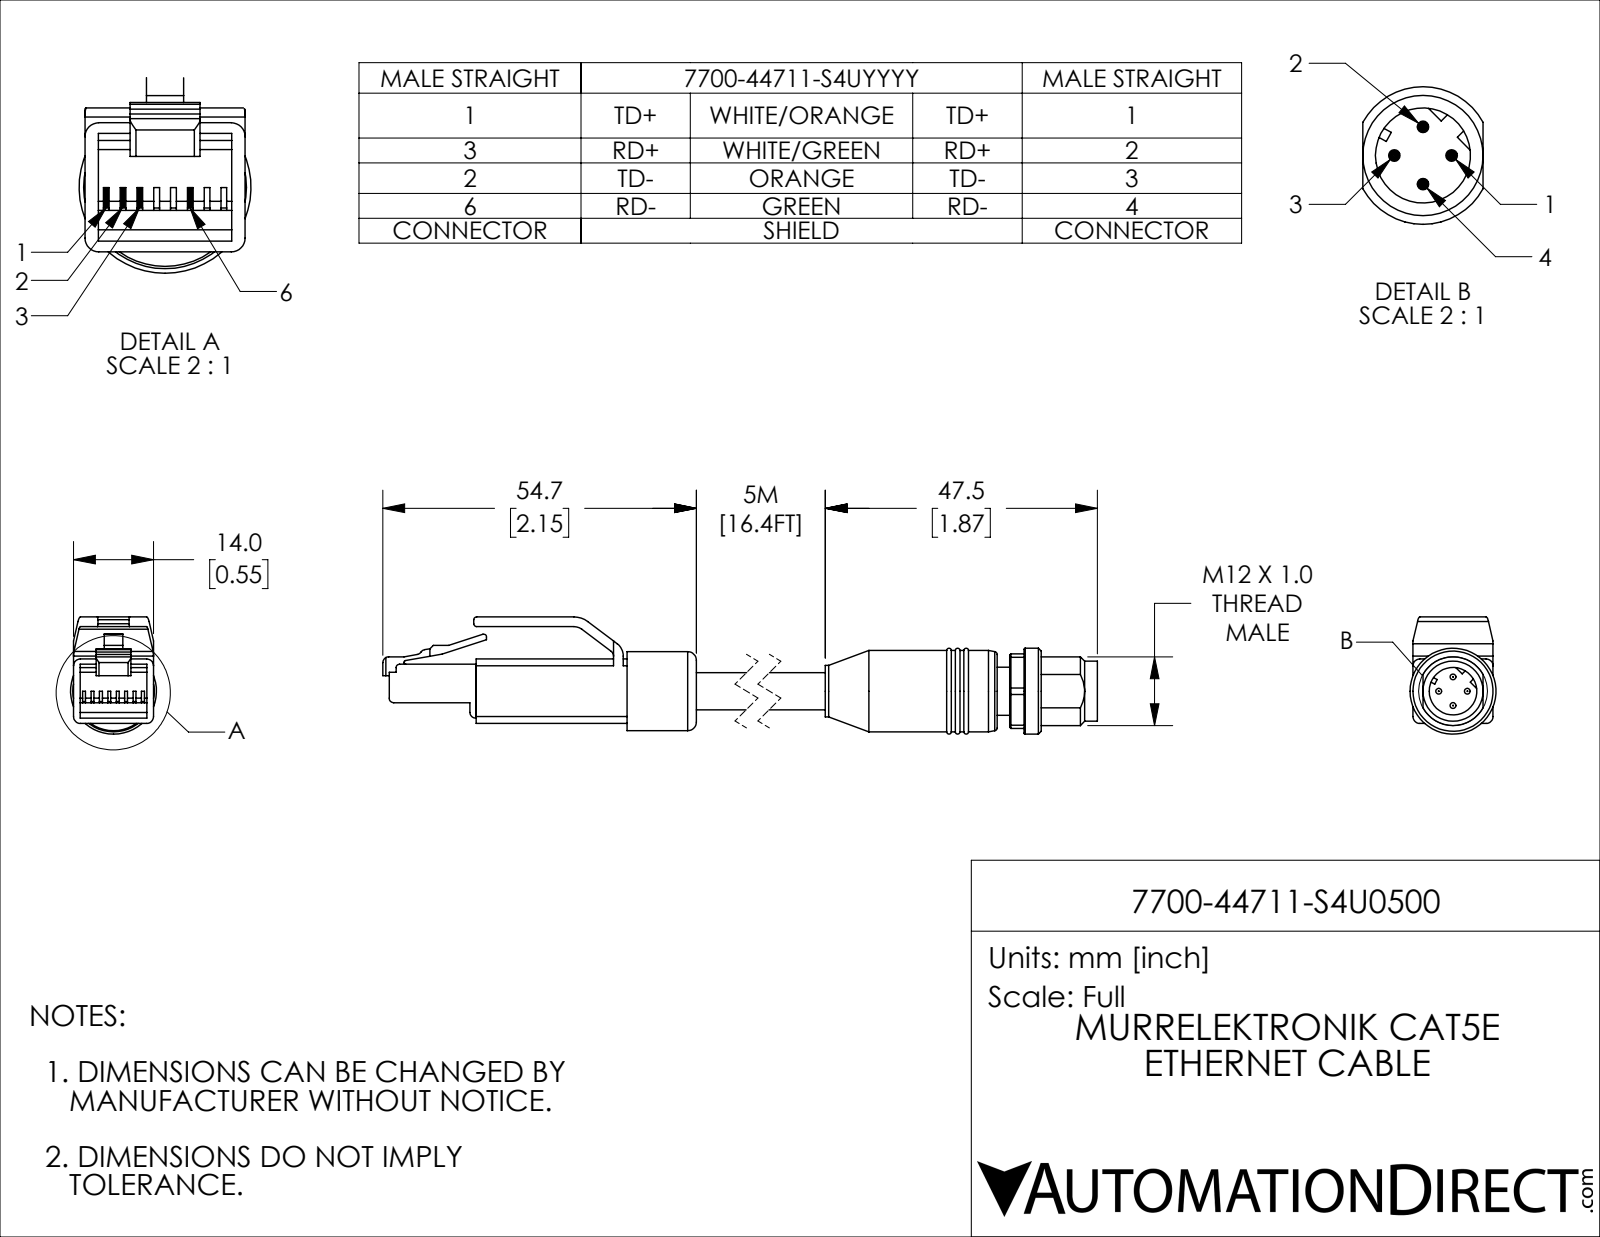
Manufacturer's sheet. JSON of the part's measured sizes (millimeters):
{"part_name": "7700-44711-S4U0500; 7700-44711-S4U0500_1; 7700-44711-S4U0500_2", "step_written_by": "SolidWorks 2021 (CONFIG_CONTROL_DESIGN)", "units": "millimeters", "bodies": {"solids": 3, "faces": 266, "planar": 151, "cylindrical": 73, "other": 42}, "overall_size": [148.7, 20.5, 15], "volume_mm3": 14900, "surface_area_mm2": 7361, "round_holes": [[8.3, 1]], "round_bosses_or_shafts": [[1, 4], [15, 1], [14.2, 1], [13.8, 1], [10.5, 1], [9, 1], [8.4, 1], [6.5, 1]], "partial_cylinders_radius": [[1.2, 6], [0.5, 5], [1, 5], [0.3, 2], [0.6, 1], [0.8, 1], [2.3, 1], [2.7, 1]], "face_to_face_distances": [11.3, 14, 1.7, 1.2, 12.8, 0.9, 10.3, 5.6, 16.9, 18.6]}
